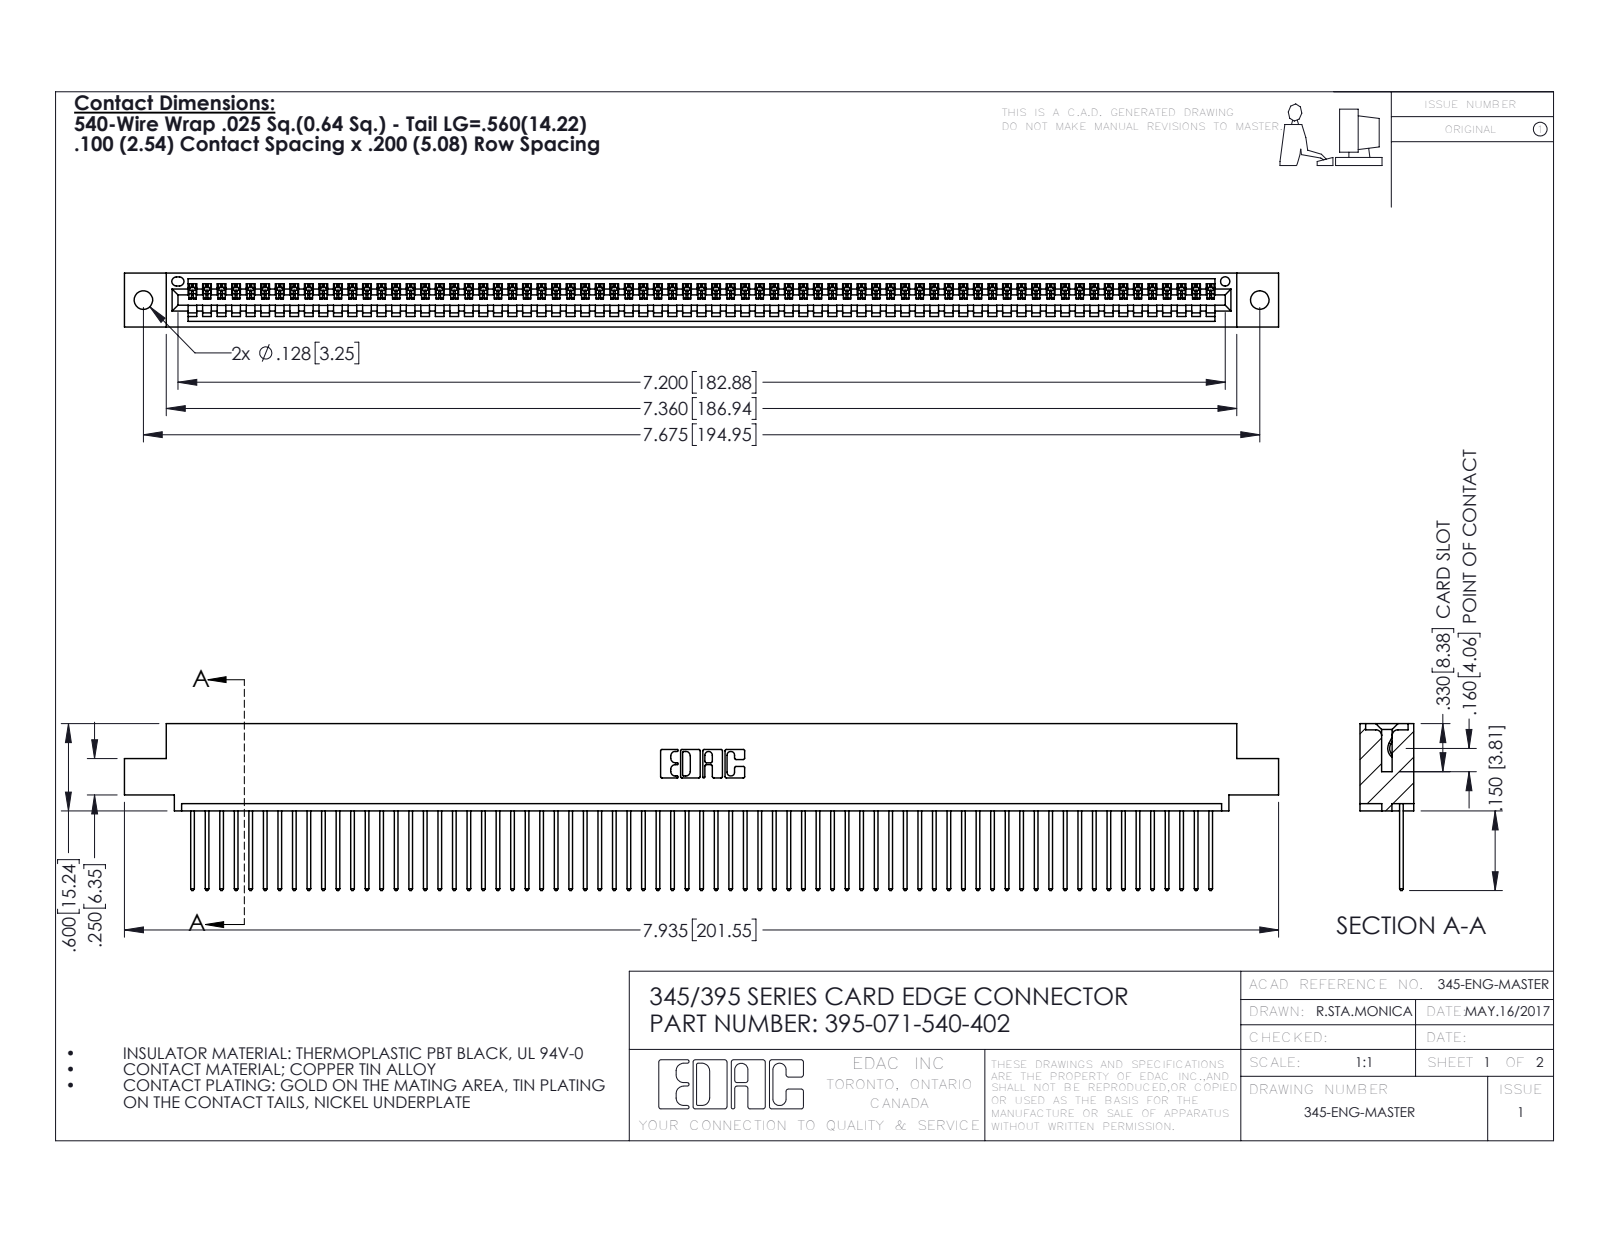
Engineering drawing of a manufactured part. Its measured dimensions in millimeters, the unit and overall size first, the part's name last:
Units: millimetres
Overall size (bounding box): 201.5 × 29.1 × 9.4
Round holes (diameter × count): ⌀3.3 ×2, ⌀1.6 ×1
Partial cylindrical surfaces — rounded edges, fillets, slot ends (radius × count): R0.2 ×142, R0.3 ×142, R0.3 ×22, R0.2 ×6, R0.8 ×6, R0.7 ×3, R0.8 ×2, R1 ×2
Main face-to-face distances: 1.8, 7.6, 9.4, 2.5, 6.9, 0.6, 5.1, 5.7, 3.8, 1.8
Hole centre spacings: 6.9, 189, 194.9
Volume: 19 370 mm³ · Surface area: 26 630 mm²
Bodies: 72 solids, 4248 faces (2924 planar, 1324 cylindrical, 0 other)
Part name (STEP PRODUCT): 395-071-540-402; 345 Part_0.110 Offset - 0.128 Dia; 345-292-001_345-293-140
STEP written by: SolidWorks 2016 (CONFIG_CONTROL_DESIGN)
